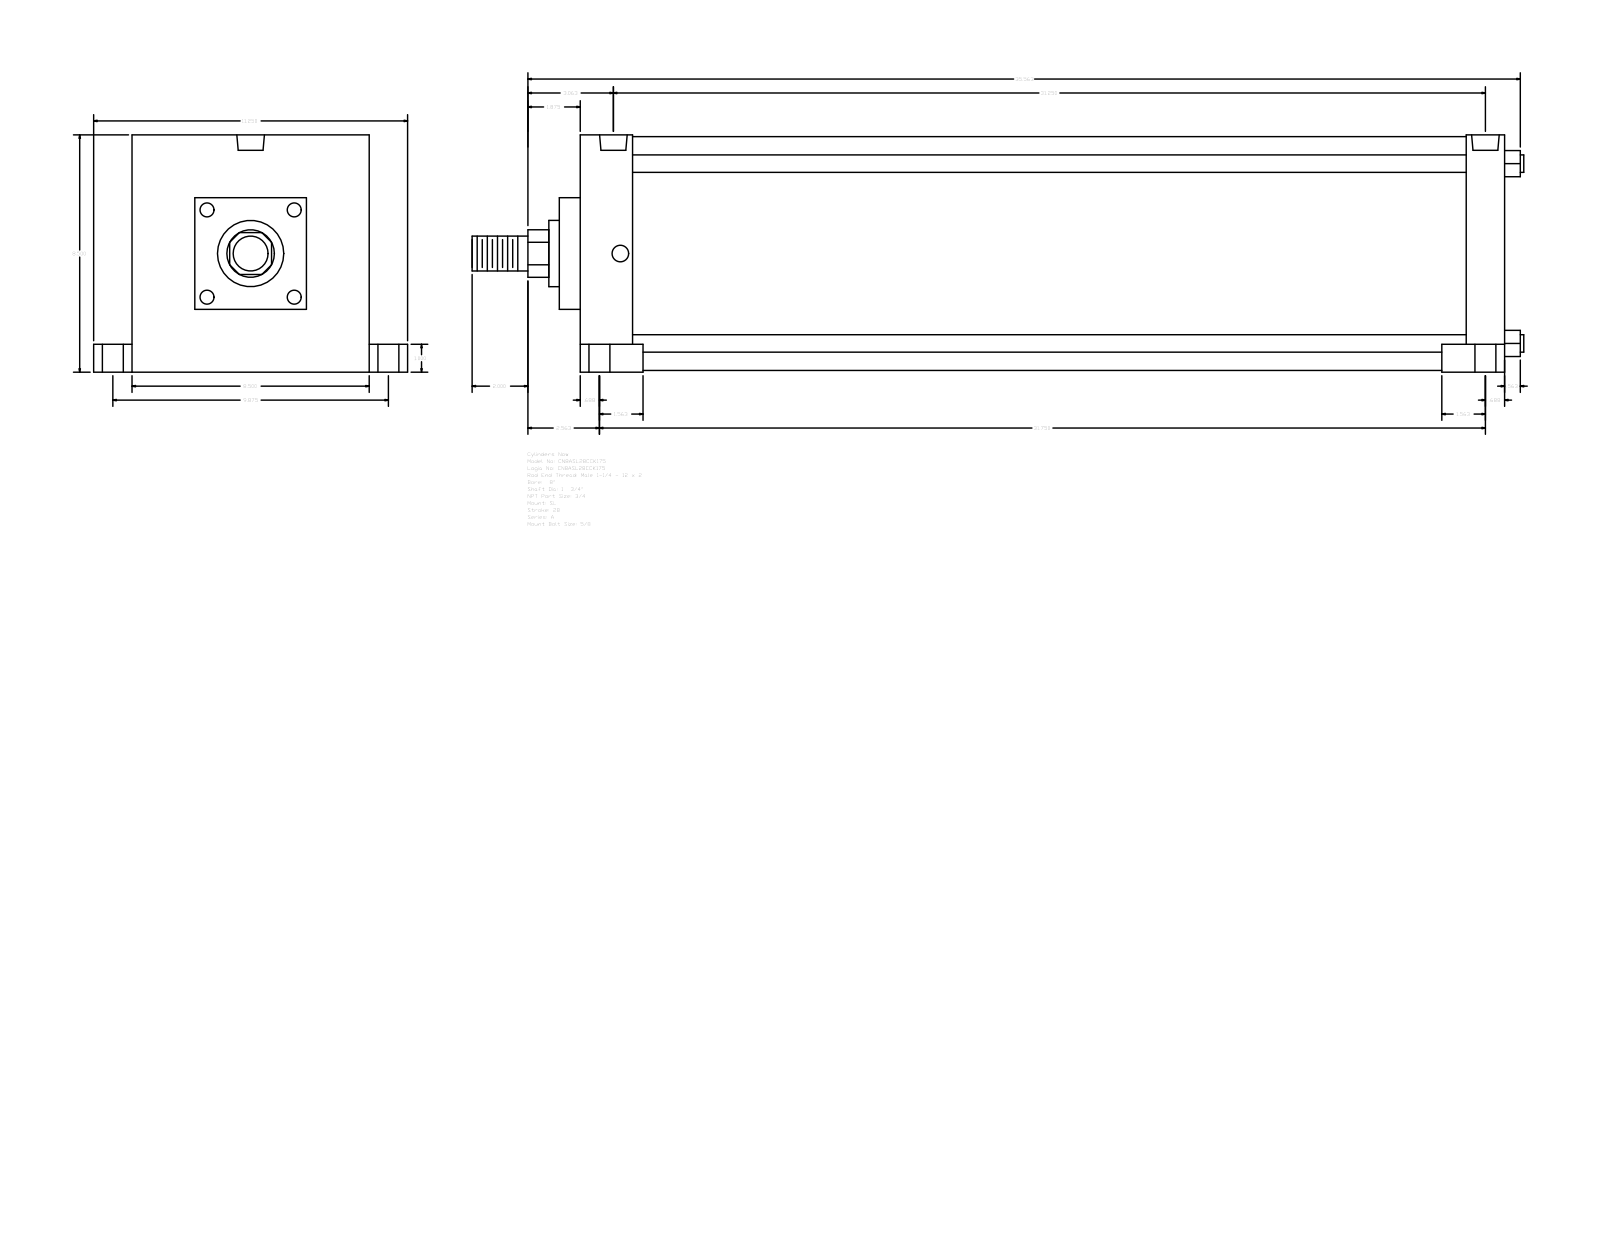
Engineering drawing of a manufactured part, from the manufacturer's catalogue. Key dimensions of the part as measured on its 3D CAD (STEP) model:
Part name (STEP PRODUCT): A_SL__0800_1.75
STEP written by: GSSL Pune (CONFIG_CONTROL_DESIGN)
Units: millimetres
Bodies: 0 solids, 117 faces (85 planar, 32 cylindrical, 0 other)
Overall size (bounding box): 957.26 × 285.75 × 215.9
Round holes (diameter × count): ⌀15.08 ×4, ⌀19.05 ×4, ⌀25.4 ×4, ⌀25.12 ×2
Round bosses / shafts (diameter × count): ⌀15.88 ×4, ⌀212.72 ×1, ⌀60.33 ×1, ⌀44.45 ×1, ⌀31.75 ×1
Partial cylindrical surfaces — rounded edges, fillets, slot ends (radius × count): R21.63 ×1
Main face-to-face distances: 841.38, 215.9, 34.92, 47.63, 793.75, 806.46, 758.83, 57.15, 19.05, 158.75
Hole centre spacings: 6.35, 125.41, 125.57, 126.05, 126.85, 250.82, 781.05, 787.4
